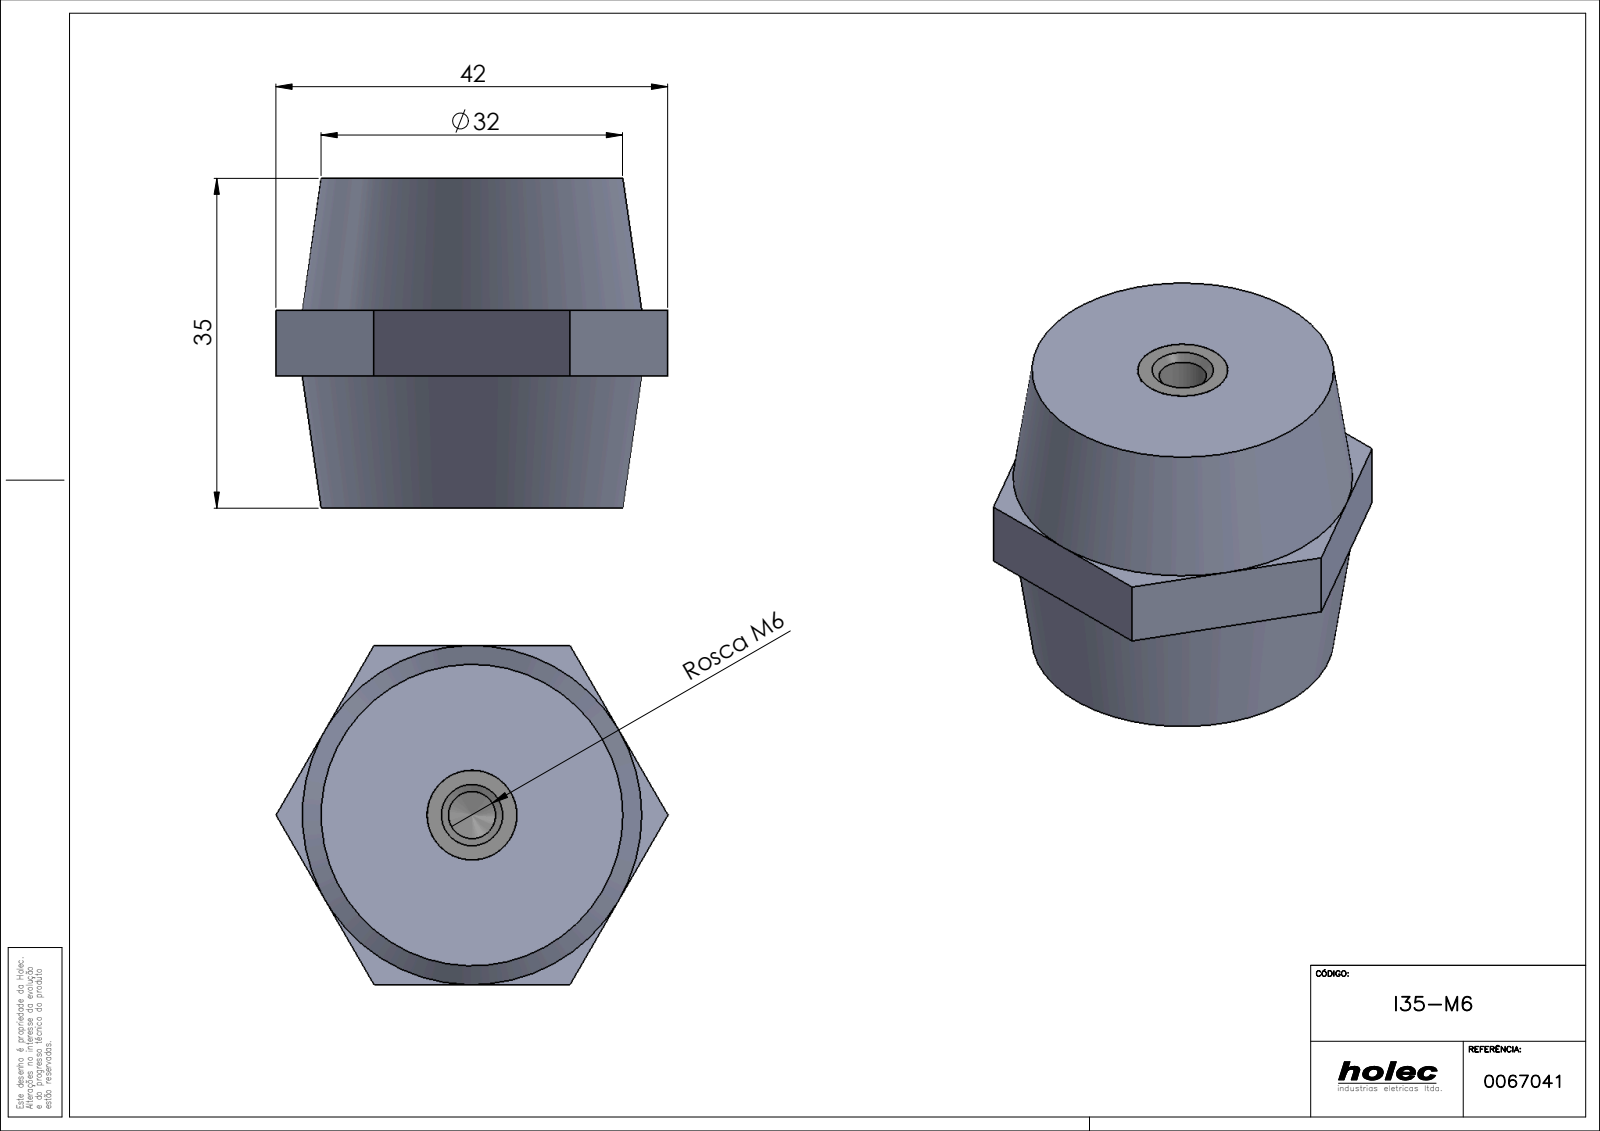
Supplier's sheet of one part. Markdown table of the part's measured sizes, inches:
| quantity | value |
| --- | --- |
| part name | PB1_0000; I35-M6; PB1_0103(PB1_0103_06) |
| STEP written by | SolidWorks 2017 (AUTOMOTIVE_DESIGN) |
| units | inches |
| bodies | 3 solids, 162 faces (82 planar, 12 cylindrical, 68 other) |
| overall size | 1.637 × 1.417 × 1.378 |
| volume | 2.016 in³ |
| surface area | 11.44 in² |
| round holes (diameter × count) | 0.197 × 1, 0.315 × 1 |
| main face-to-face distances | 1.378, 1.417, 0.375, 1.063, 0.551, 0.827, 1.063, 0.098, 0.217, 0.315 |
